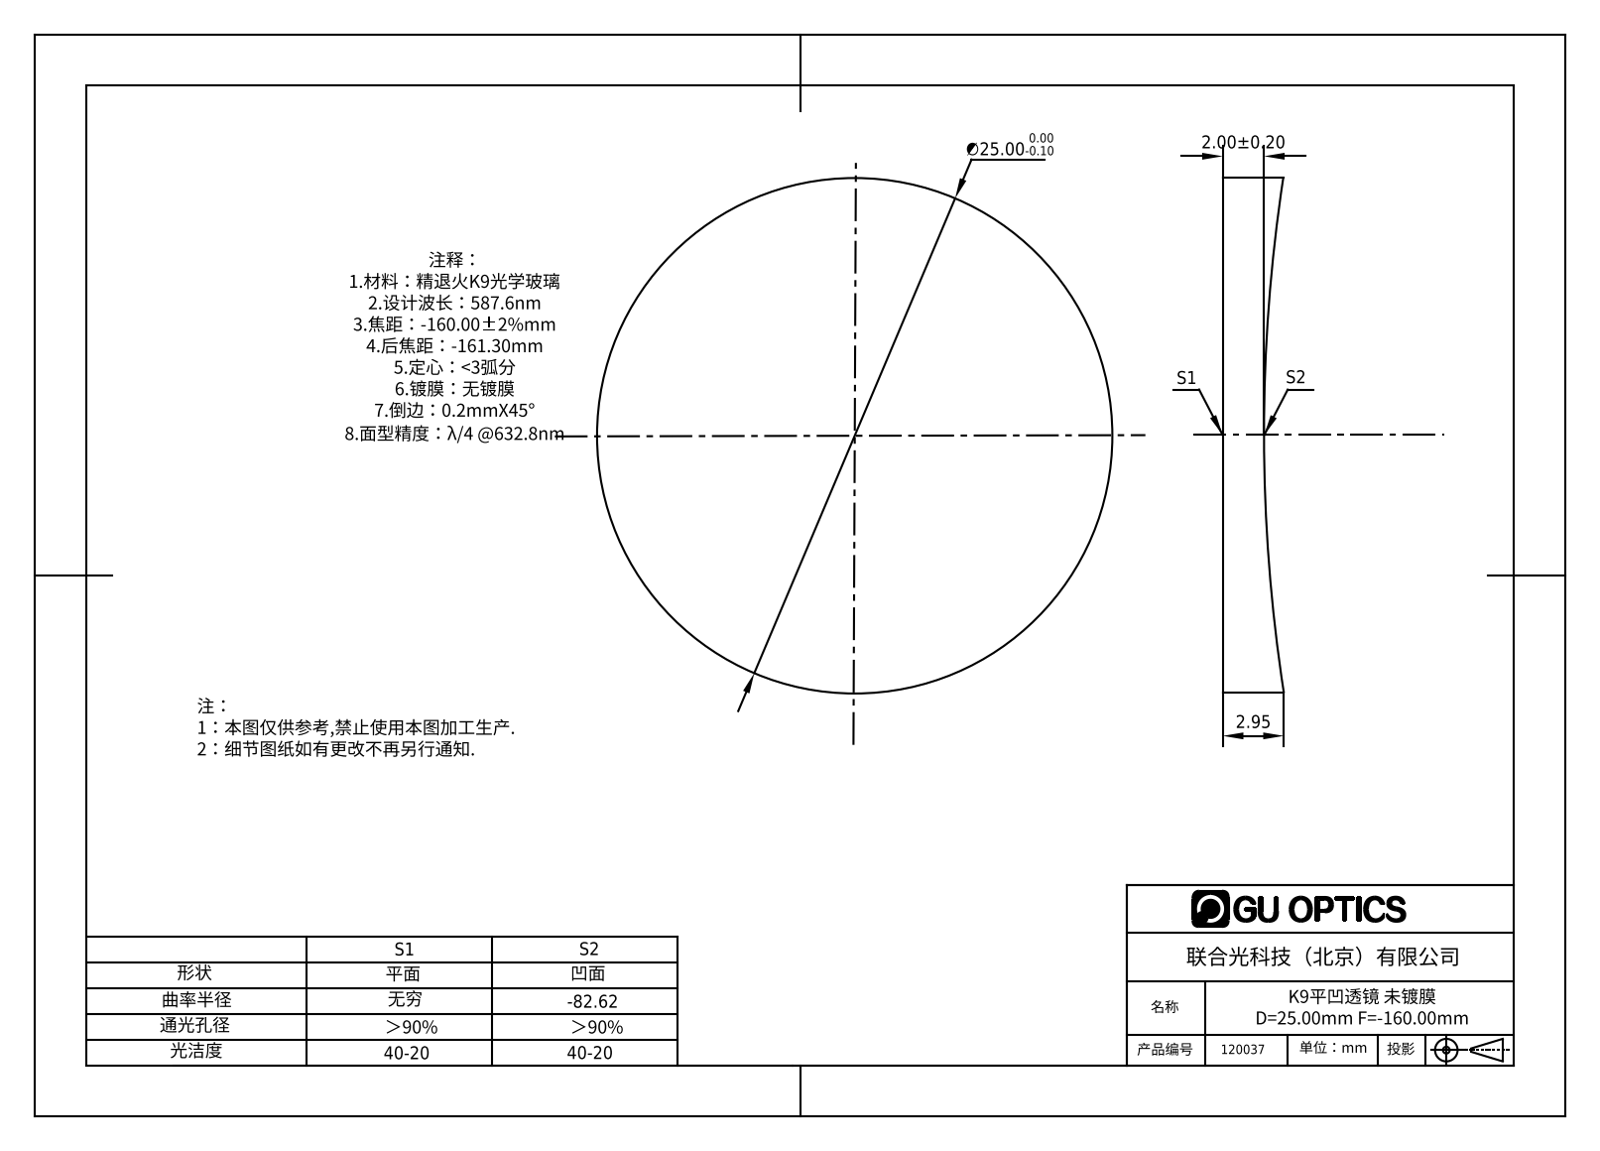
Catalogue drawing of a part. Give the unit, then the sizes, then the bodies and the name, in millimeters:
Units: millimetres
Overall size (bounding box): 25 × 25 × 2.94
Round bosses / shafts (diameter × count): ⌀25 ×1
Volume: 1 211 mm³ · Surface area: 1 215 mm²
Bodies: 1 solid, 5 faces (1 planar, 2 cylindrical, 2 other)
Part name (STEP PRODUCT): 120037
STEP written by: SolidWorks 2016 (AUTOMOTIVE_DESIGN)
